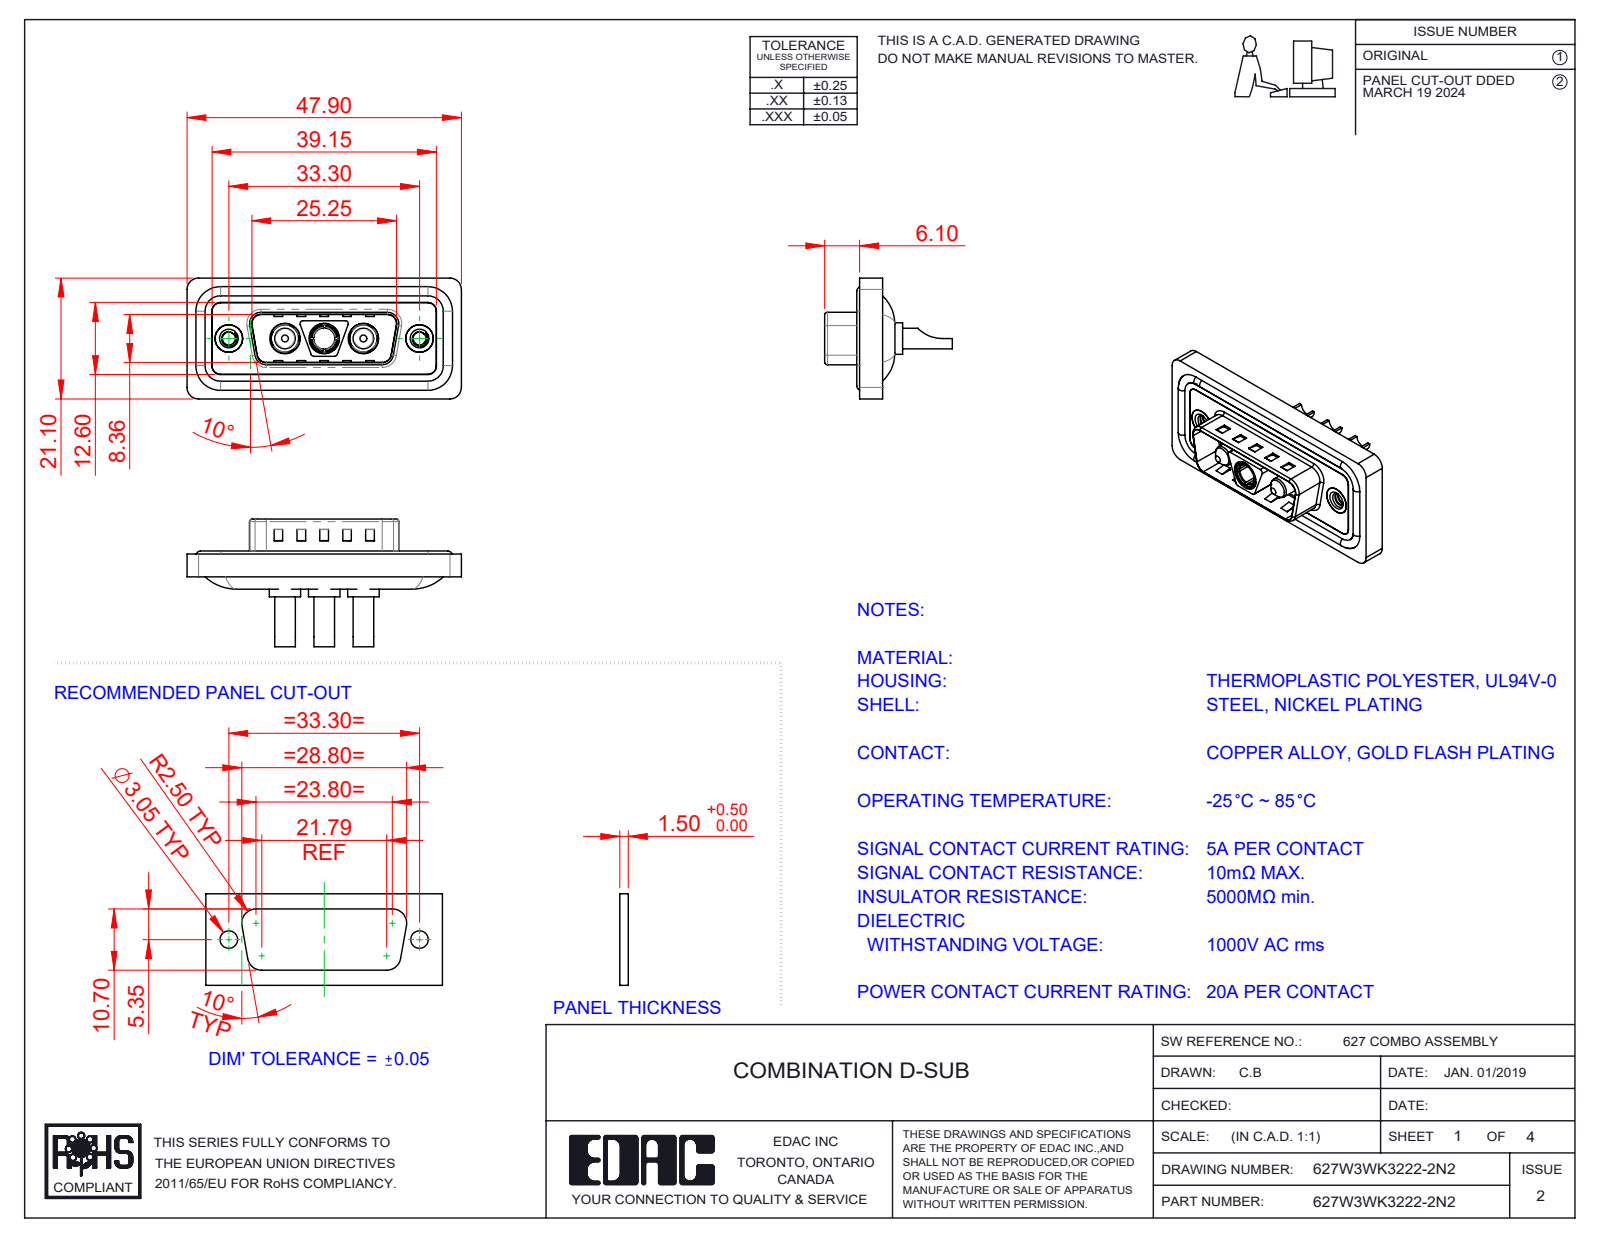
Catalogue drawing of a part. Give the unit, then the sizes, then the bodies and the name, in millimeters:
Units: millimetres
Overall size (bounding box): 47.9 × 22.3 × 21.1
Round holes (diameter × count): ⌀2.7 ×3, ⌀4.85 ×3, ⌀5.3 ×3, ⌀2.26 ×2, ⌀4 ×2, ⌀4.8 ×2, ⌀5 ×2, ⌀3.7 ×1
Round bosses / shafts (diameter × count): ⌀1.6 ×4, ⌀5.5 ×3, ⌀5.2 ×3, ⌀4.75 ×3, ⌀3.75 ×3, ⌀3.6 ×3, ⌀4.9 ×2, ⌀4.96 ×1
Partial cylindrical surfaces — rounded edges, fillets, slot ends (radius × count): R1.5 ×26, R2 ×20, R0.5 ×12, R1.6 ×8, R0.25 ×4, R0.6 ×4, R0.65 ×4, R0.9 ×4
Main face-to-face distances: 0.4, 1.1, 0.5, 1.5, 1.6, 3.1, 2.9, 4, 0.82, 9.58
Hole centre spacings: 6.85, 9.8, 16.65, 23.5, 13.7, 33.3
Volume: 5 726 mm³ · Surface area: 9 374 mm²
Bodies: 13 solids, 630 faces (240 planar, 259 cylindrical, 131 other)
Part name (STEP PRODUCT): 627Combo Waterproof Housing_15 Contacts; Power Pin_20A SC; 627Combo Shell Rear_15 Contacts; 627Combo Threaded Rivet_2 (+4 more)
STEP written by: SolidWorks 2023 (CONFIG_CONTROL_DESIGN)
